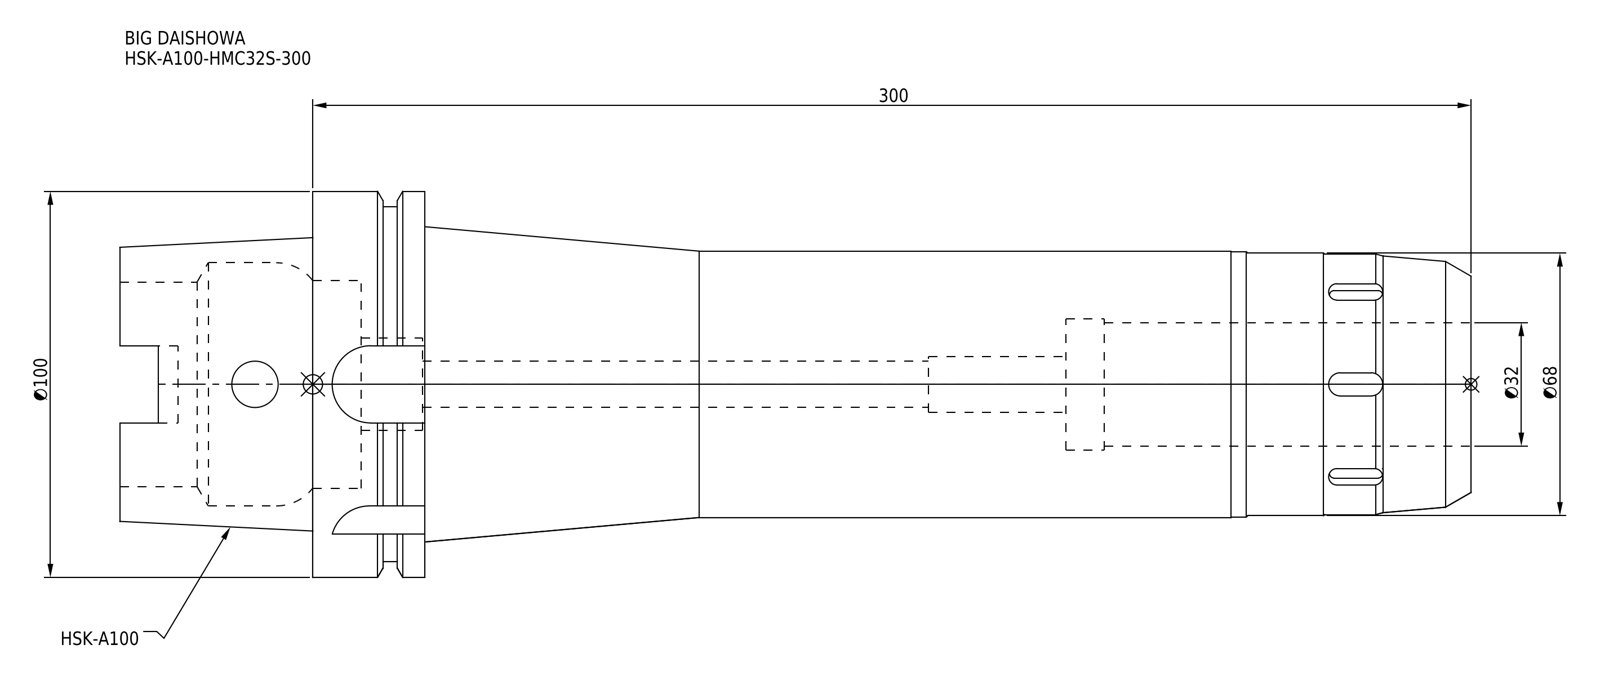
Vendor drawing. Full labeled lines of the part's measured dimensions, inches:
Part name (STEP PRODUCT): HSK-A100-HMC32S-300
STEP written by: CREO PARAMETRIC BY PTC INC, 2016380 (AUTOMOTIVE_DESIGN)
Units: inches
Bodies: 1 solid, 146 faces (60 planar, 62 cylindrical, 24 other)
Overall size (bounding box): 13.78 × 3.937 × 3.937
Volume: 72.86 in³ · Surface area: 193.9 in²
Round holes (diameter × count): ⌀0.472 ×2, ⌀0.571 ×1, ⌀0.945 ×1, ⌀1.26 ×1, ⌀1.339 ×1, ⌀2.087 ×1, ⌀2.118 ×1, ⌀2.48 ×1
Round bosses / shafts (diameter × count): ⌀3.937 ×1, ⌀3.622 ×1, ⌀2.717 ×1, ⌀2.705 ×1, ⌀2.677 ×1, ⌀2.657 ×1
Partial cylindrical surfaces — rounded edges, fillets, slot ends (radius × count): R0.118 ×12, R0.192 ×4, R0.394 ×4
Main face-to-face distances: 1.142, 0.652, 0.49, 10.669, 11.321, 11.811, 13.78, 3.11, 2.459, 1.969
